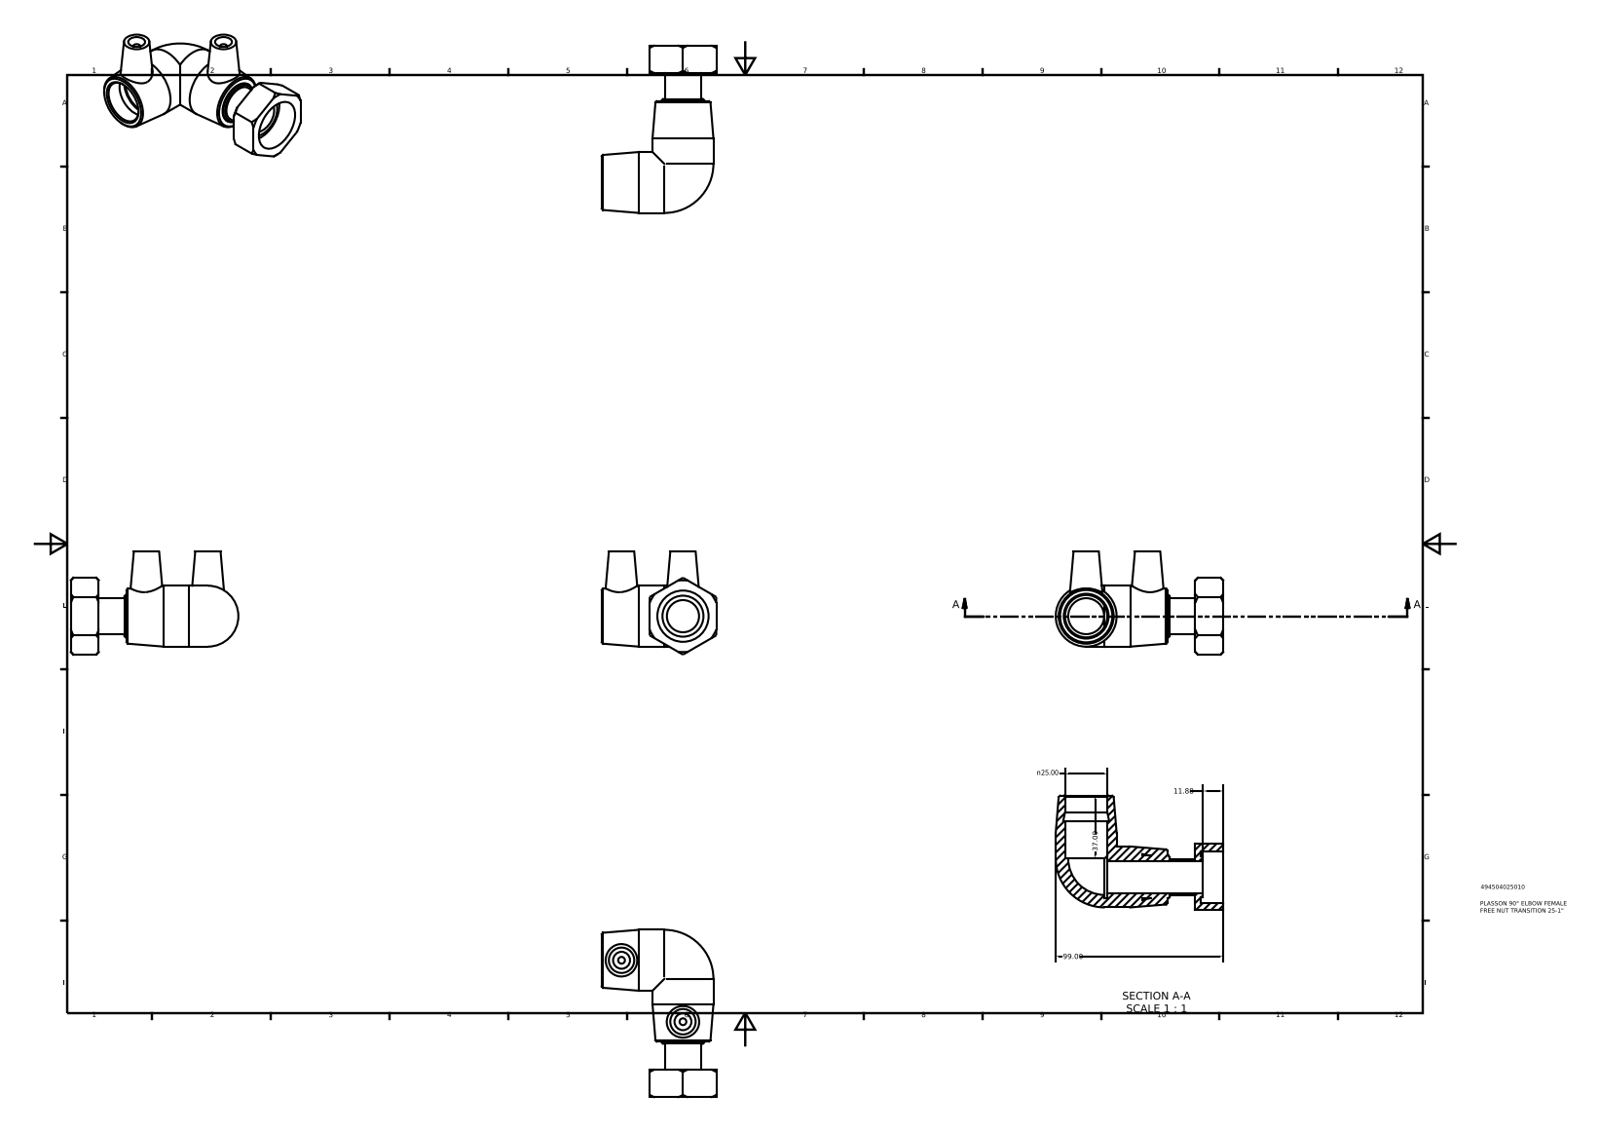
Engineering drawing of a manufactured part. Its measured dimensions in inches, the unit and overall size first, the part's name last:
Units: inches
Overall size (bounding box): 3.898 × 2.664 × 2.391
Round holes (diameter × count): ⌀0.394 ×2, ⌀0.748 ×1, ⌀0.984 ×1, ⌀1.193 ×1
Round bosses / shafts (diameter × count): ⌀1.417 ×2, ⌀0.157 ×2, ⌀0.984 ×1, ⌀0.954 ×1, ⌀0.835 ×1
Main face-to-face distances: 1.549, 0.65, 0.78, 0.13, 0.52, 1.299, 0.052, 1.457, 1.398, 2.047
Hole centre spacings: 2.021
Volume: 4.515 in³ · Surface area: 46.03 in²
Bodies: 1 solid, 63 faces (24 planar, 15 cylindrical, 24 other)
Part name (STEP PRODUCT): 494504025010
STEP written by: Autodesk Inventor 2015 (AUTOMOTIVE_DESIGN)
